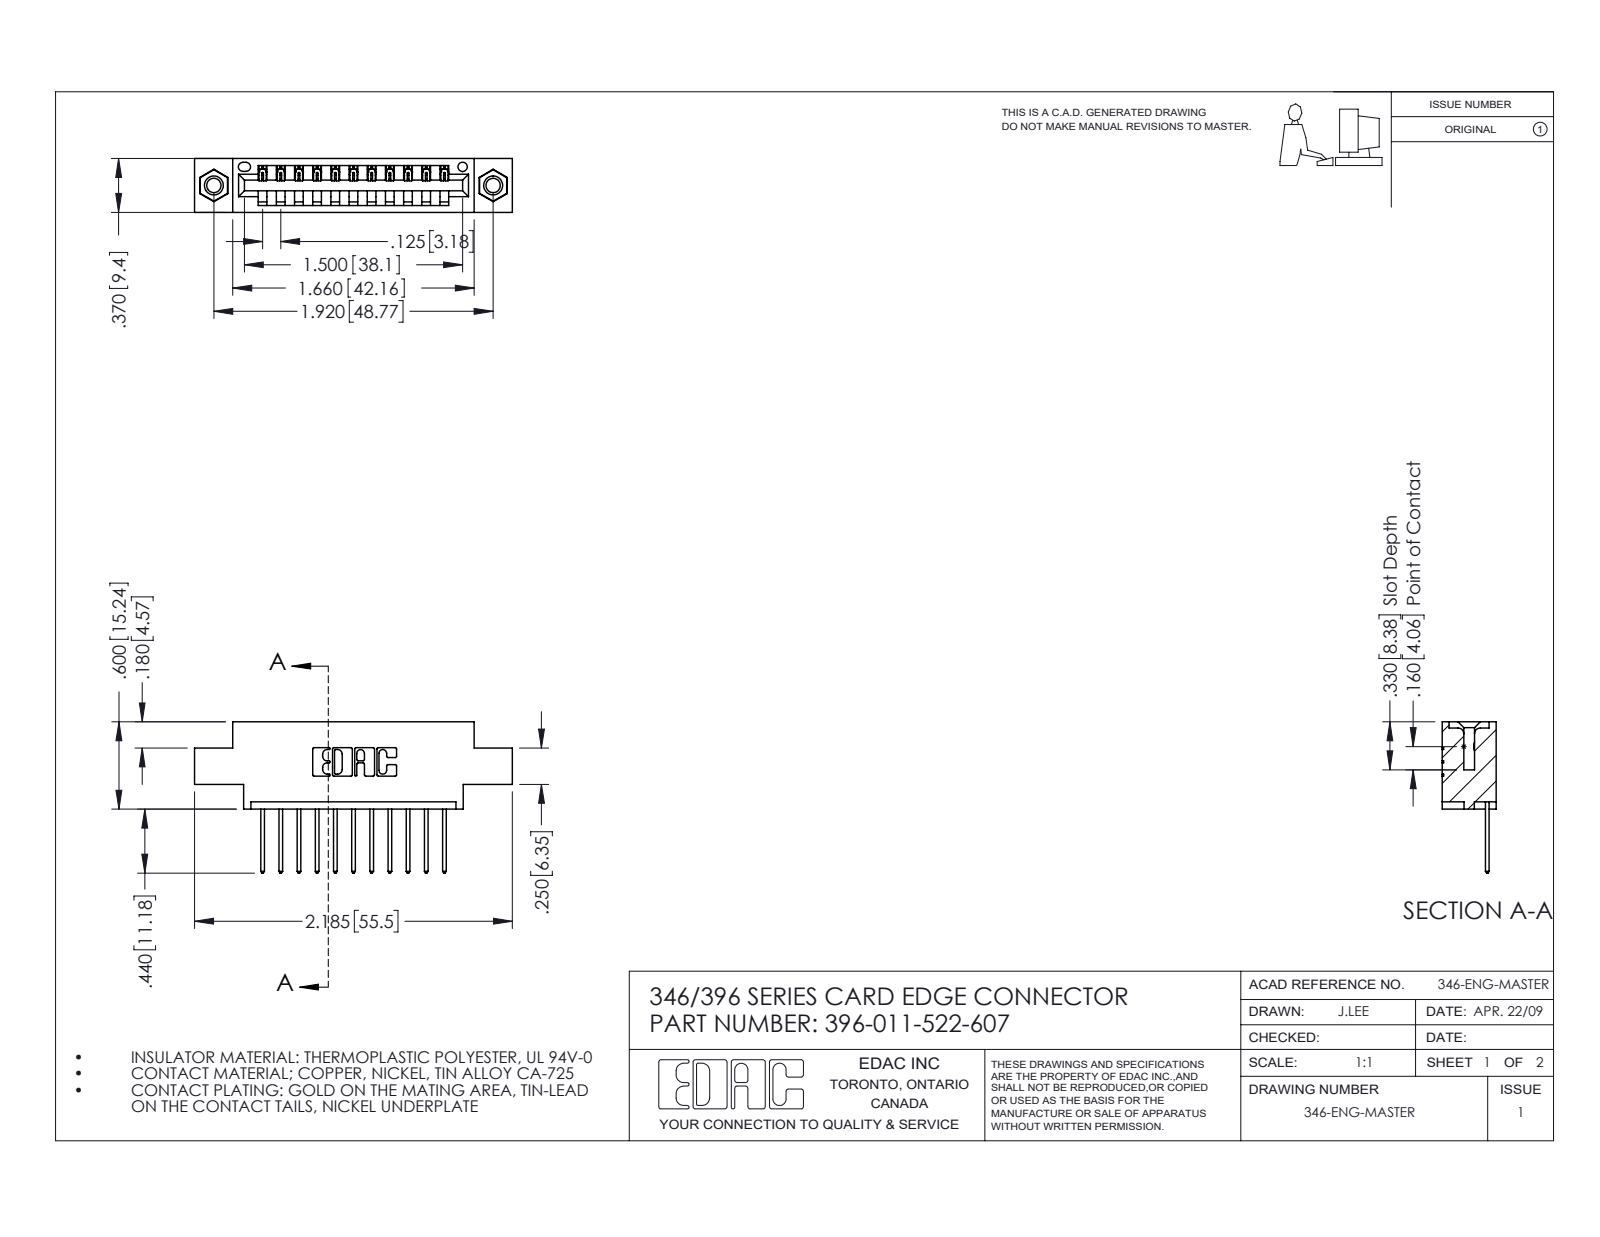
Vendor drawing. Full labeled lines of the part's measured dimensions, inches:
Part name (STEP PRODUCT): 396-011-522-607; 346 Part_0.170 Offset - 0.156 Dia-TI; 345-250-001_345-250-005-103; 345-292-001_345-293-122
STEP written by: SolidWorks 2016 (CONFIG_CONTROL_DESIGN)
Units: inches
Bodies: 14 solids, 824 faces (552 planar, 256 cylindrical, 16 other)
Overall size (bounding box): 2.185 × 1.04 × 0.37
Volume: 0.301 in³ · Surface area: 9.402 in²
Round holes (diameter × count): ⌀0.098 ×2, ⌀0.125 ×2, ⌀0.156 ×2, ⌀0.064 ×1
Round bosses / shafts (diameter × count): ⌀0.155 ×2
Partial cylindrical surfaces — rounded edges, fillets, slot ends (radius × count): R0.006 ×22, R0.01 ×22, R0.01 ×22, R0.007 ×6, R0.031 ×6, R0.026 ×3, R0.031 ×2, R0.04 ×2
Main face-to-face distances: 0.25, 0.37, 0.048, 0.322, 0.072, 0.298, 0.025, 0.222, 0.148, 0.1
Hole centre spacings: 0.246, 1.715, 1.92
